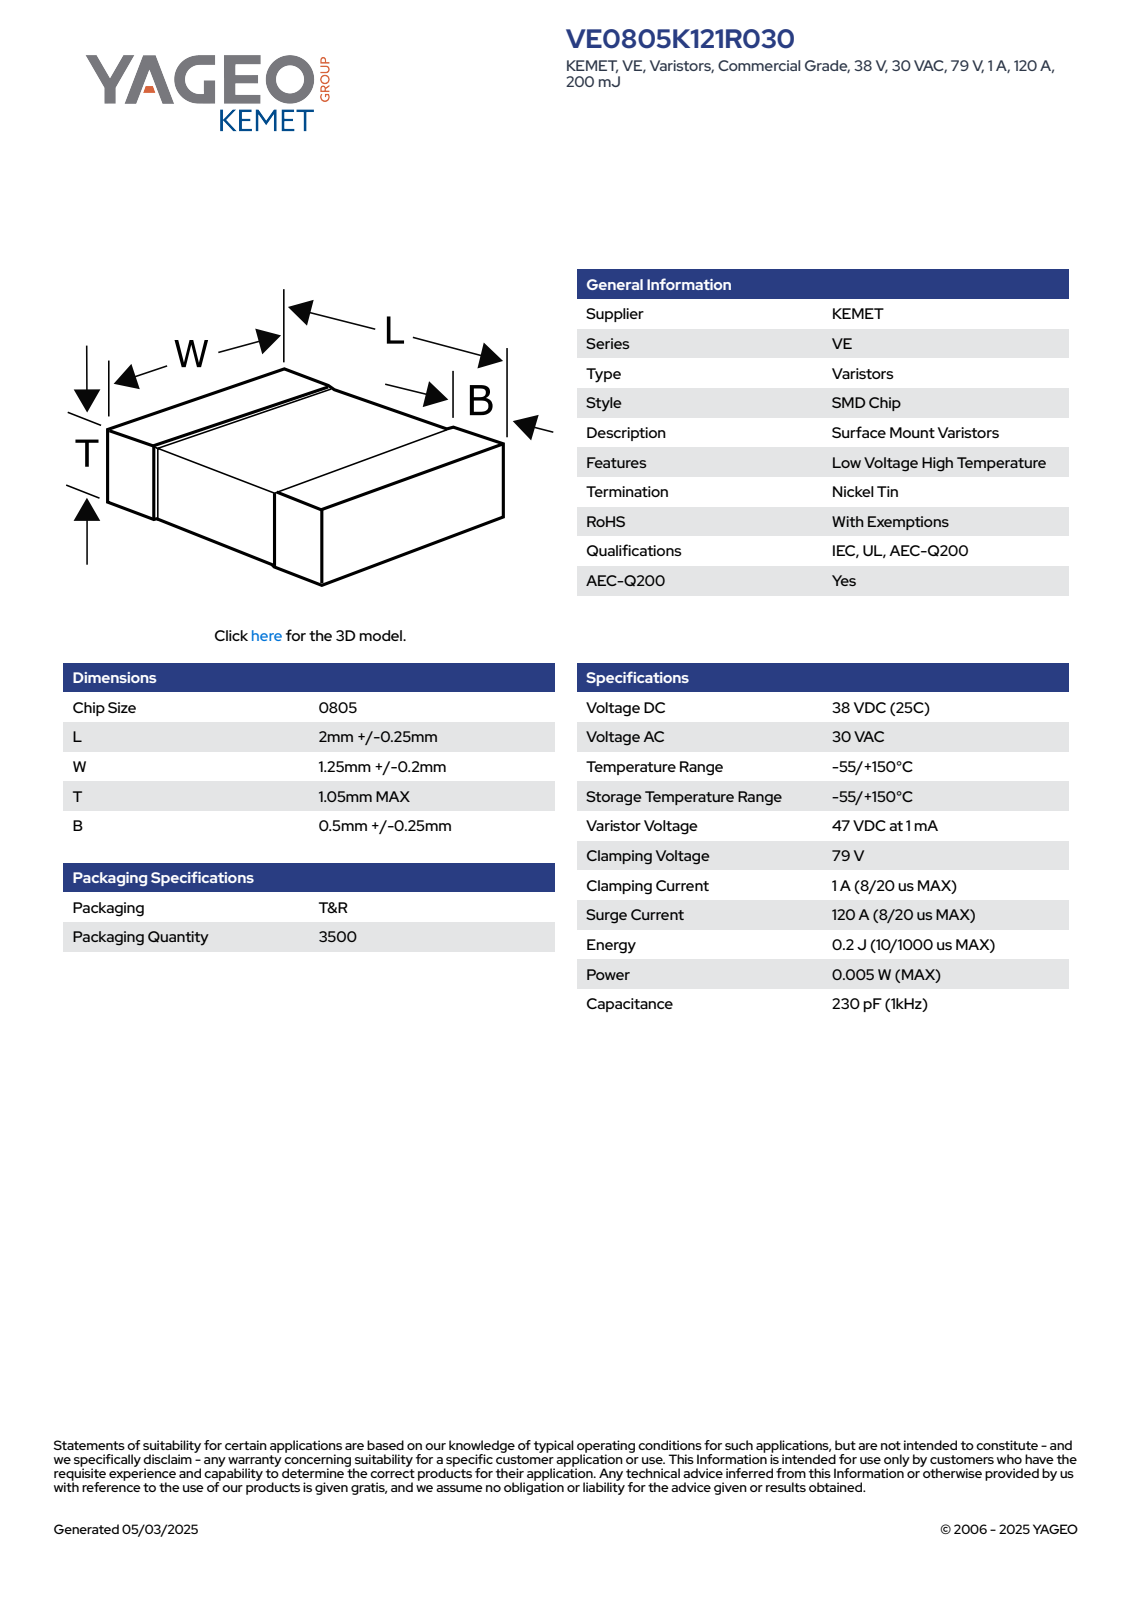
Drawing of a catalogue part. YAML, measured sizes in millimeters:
part_name: "VS_SMD_0805_L2.25W1.45T1.05B0.75"
step_written_by: "SolidWorks 2014 (AUTOMOTIVE_DESIGN)"
units: millimeters
bodies: {solids: 4, faces: 129, planar: 71, cylindrical: 42, other: 16}
overall_size: [2.25, 1.45, 1.05]
volume: 3
surface_area: 14
face_to_face_distances: [1.02, 1.05, 1.42, 2.25, 1.45, 0.99, 1.39, 1, 1.25, 1.22]
